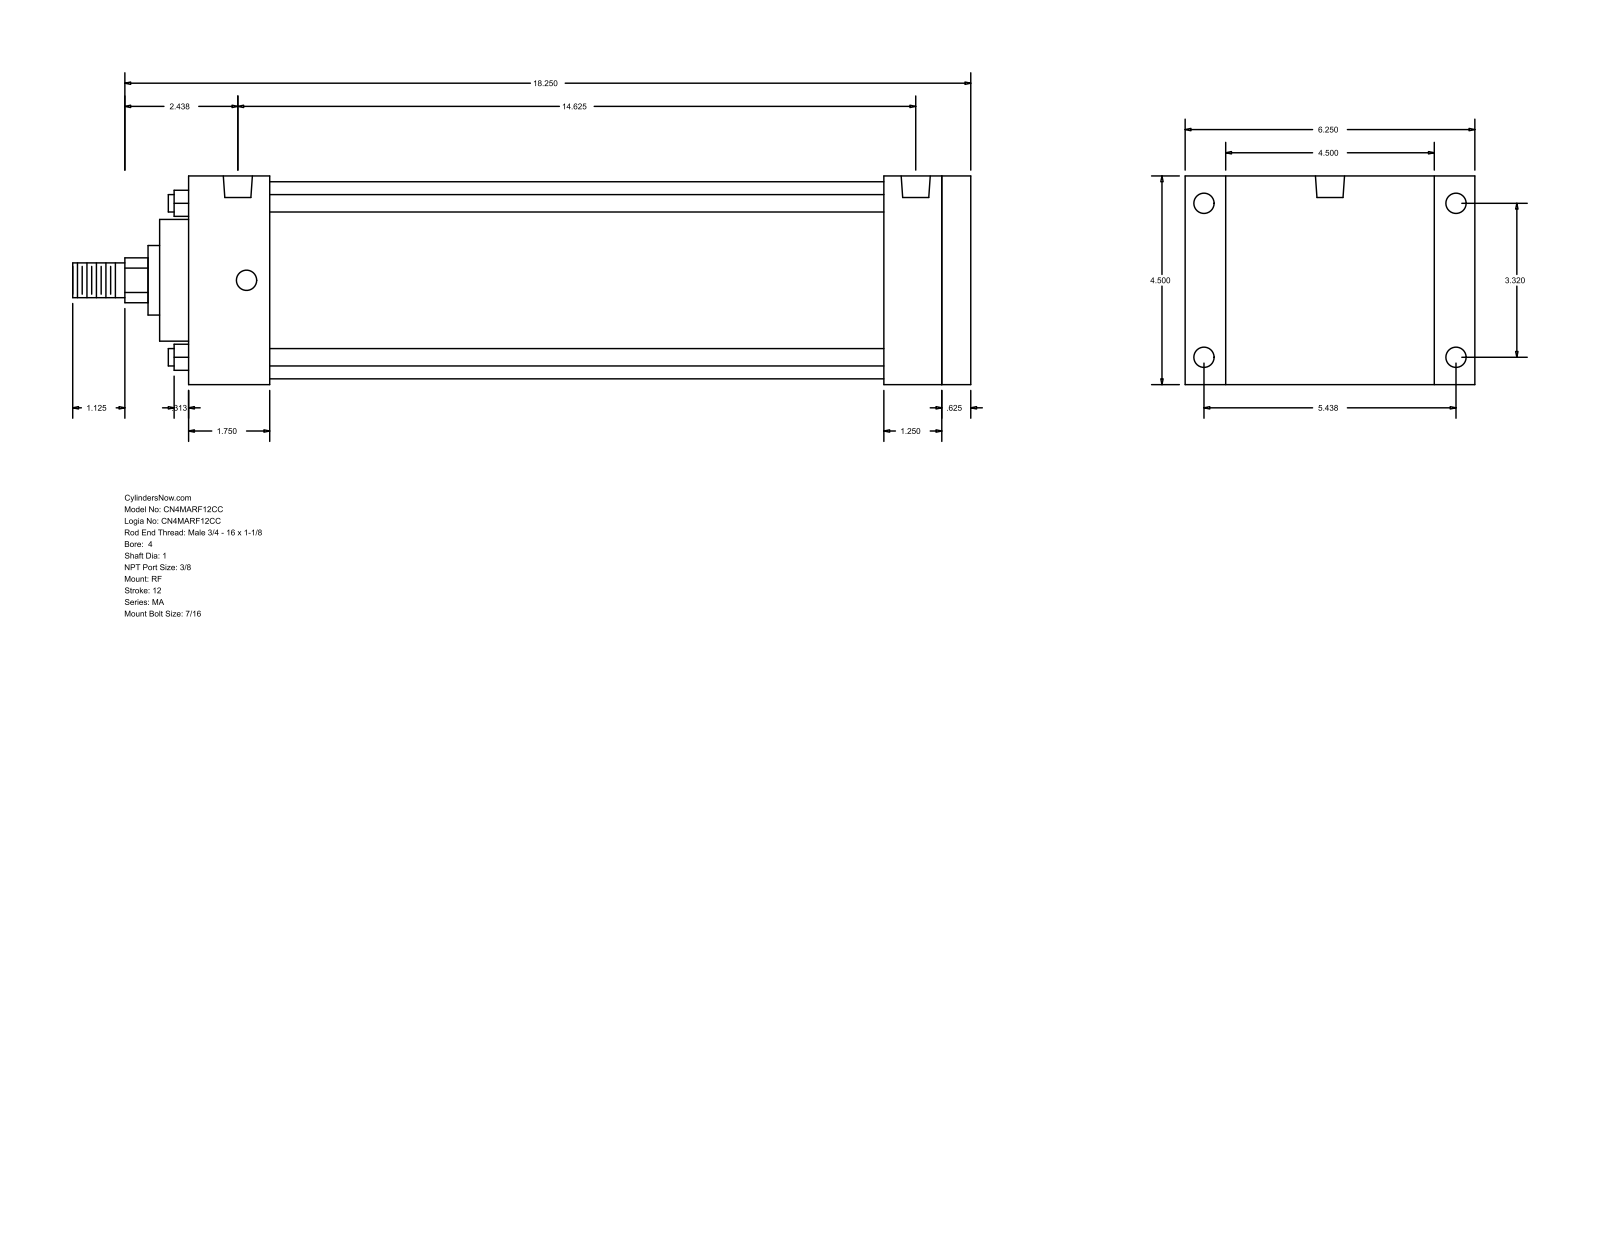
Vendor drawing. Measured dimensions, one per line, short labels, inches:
name: MA_RF__0400_1
written by: GSSL Pune (CONFIG_CONTROL_DESIGN)
unit: in
bodies: 0 solids, 94 faces (65 planar, 29 cylindrical, 0 other)
size: 19.375 × 6.25 × 4.5
holes: 8× ⌀0.437, 2× ⌀0.627
bosses: 4× ⌀0.375, 1× ⌀4.25, 1× ⌀2.625, 1× ⌀1.5, 1× ⌀1, 1× ⌀0.75
rounds: 1× R0.484
face distances: 4.5, 16.875, 0.625, 16.25, 1.875, 0.875, 5.375, 15, 1.25, 1.75
hole spacings: 3.32, 5.438, 6.371, 14.25, 0.187, 0.188, 14.437, 14.438
